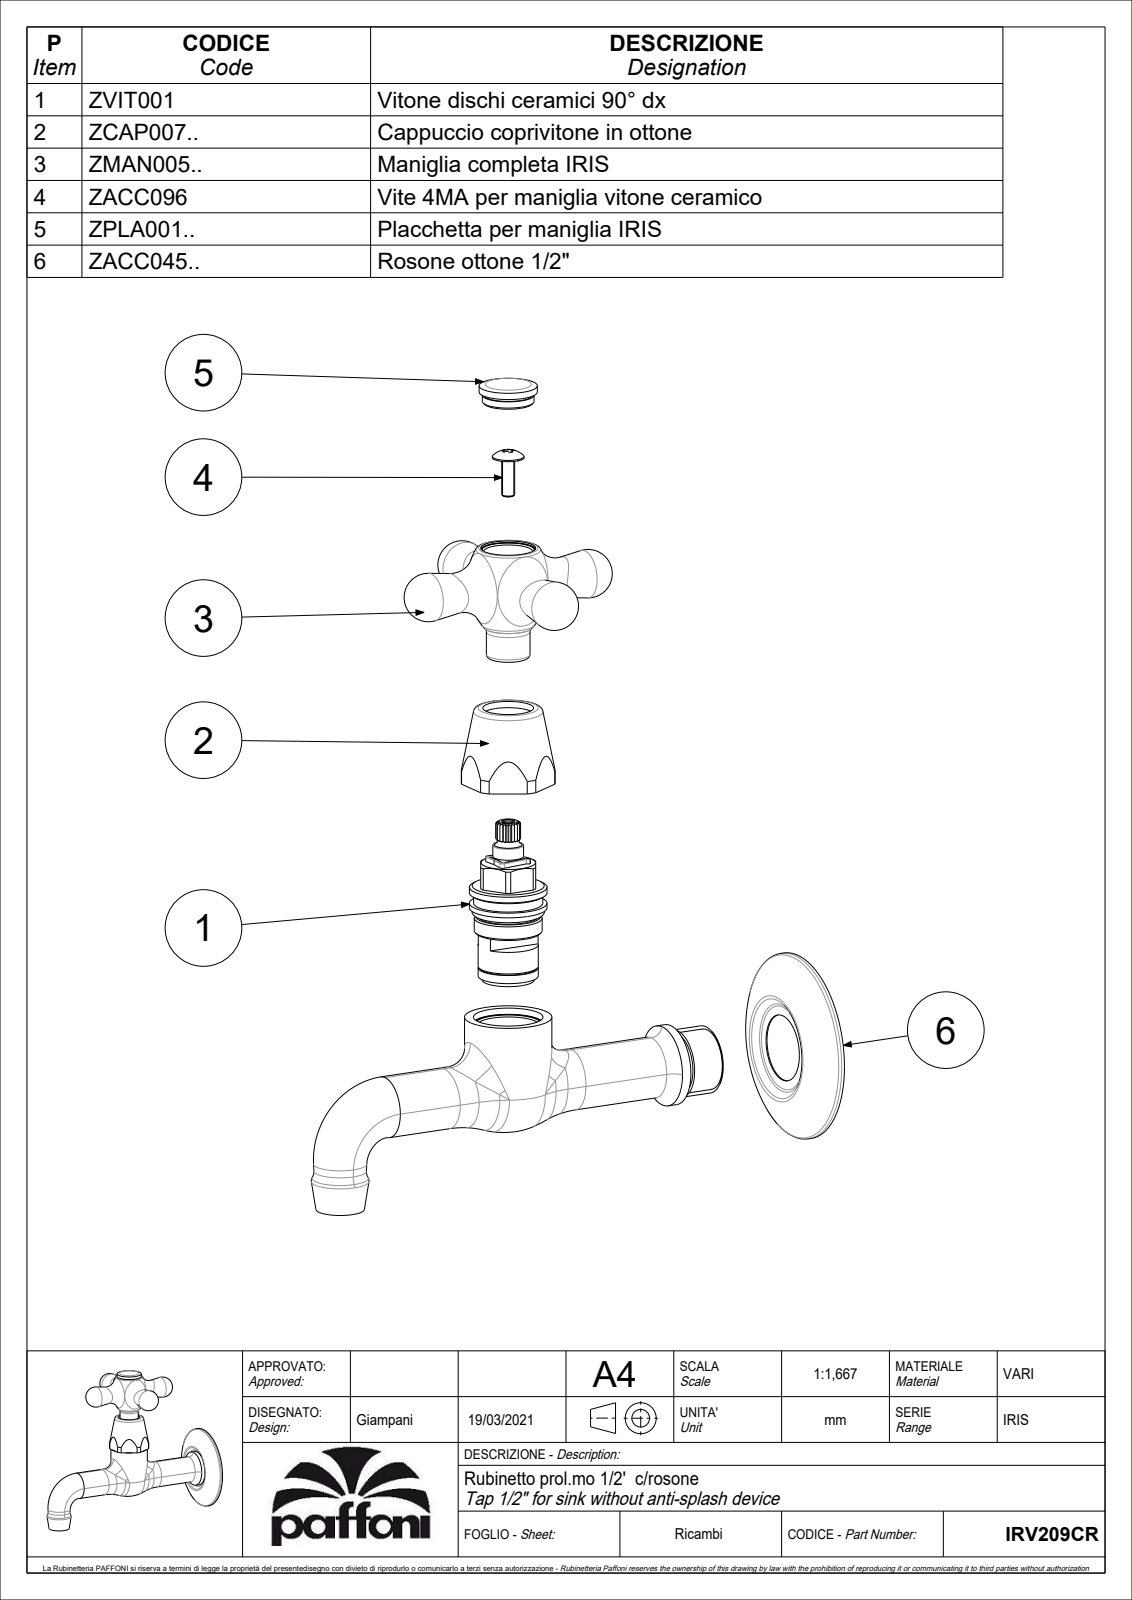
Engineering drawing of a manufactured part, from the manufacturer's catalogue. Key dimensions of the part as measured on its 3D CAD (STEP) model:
Part name (STEP PRODUCT): IRV209CR
STEP written by: CREO PARAMETRIC BY PTC INC, 2020044 (CONFIG_CONTROL_DESIGN)
Units: millimetres
Bodies: 1 solid, 154 faces (24 planar, 18 cylindrical, 112 other)
Overall size (bounding box): 139.92 × 112.2 × 72
Volume: 104 947 mm³ · Surface area: 24 049 mm²
Round bosses / shafts (diameter × count): ⌀58 ×1, ⌀27 ×1, ⌀25 ×1, ⌀21 ×1, ⌀18 ×1, ⌀13.5 ×1
Partial cylindrical surfaces — rounded edges, fillets, slot ends (radius × count): R14.5 ×1
Main face-to-face distances: 7.7, 26.5, 77.5, 57.75, 84.25, 50.05, 76.55, 13, 5.3, 44.75
